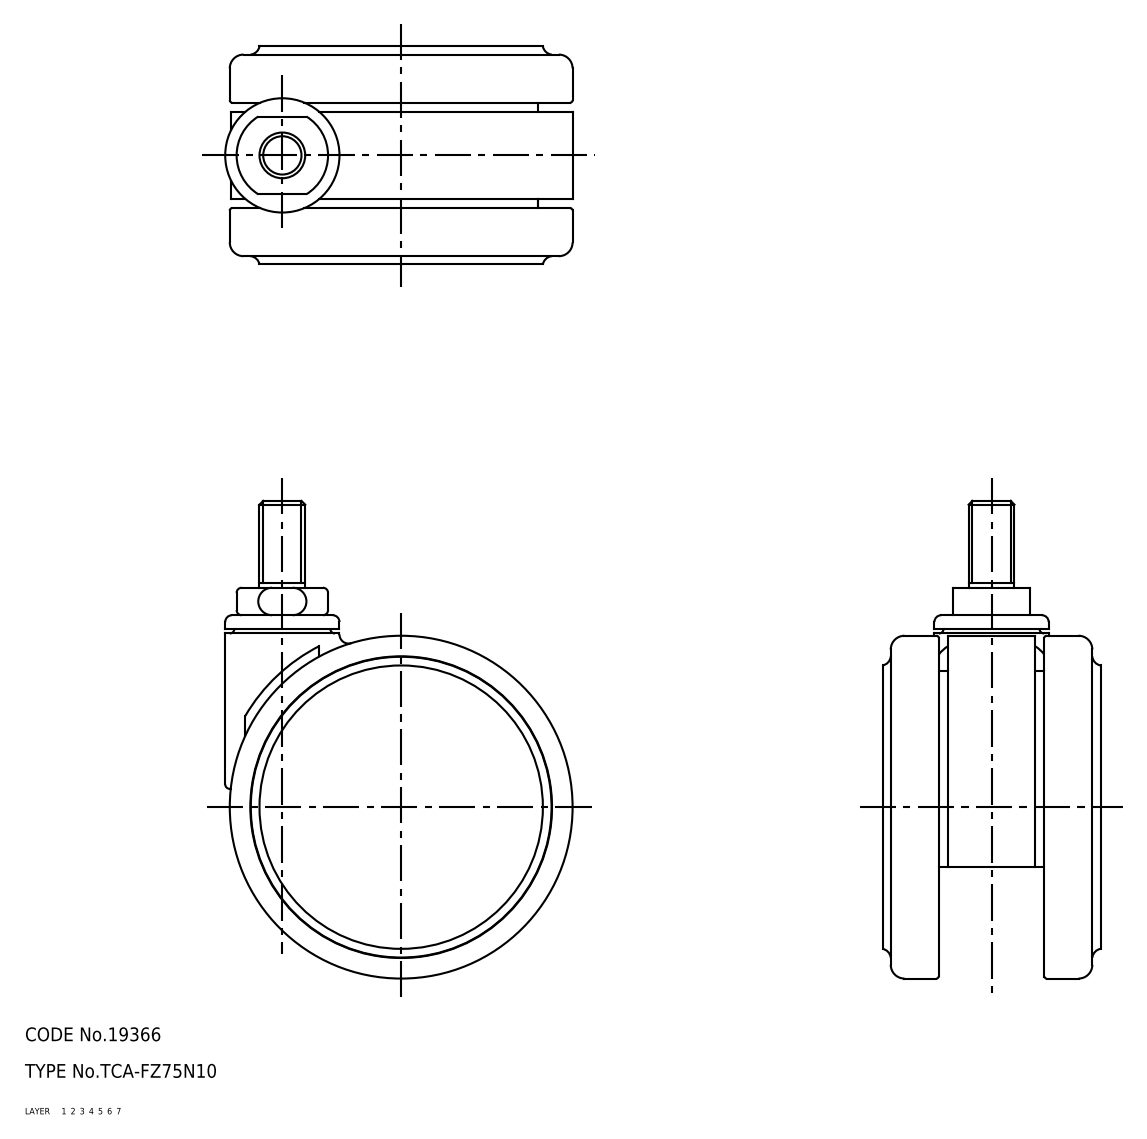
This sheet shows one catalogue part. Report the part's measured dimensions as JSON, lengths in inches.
{"part_name": "caster; TCA-FZ75N10", "step_written_by": "SolidWorks 2015 (AUTOMOTIVE_DESIGN)", "units": "inches", "bodies": {"solids": 1, "faces": 1801, "planar": 425, "cylindrical": 766, "other": 610}, "overall_size": [4.114, 2.992, 1.878], "volume_in3": 6.903, "surface_area_in2": 106.7, "round_holes": [[0.256, 1], [0.315, 1], [0.319, 1], [0.335, 1], [0.402, 1], [0.433, 1], [0.669, 1], [0.713, 1], [0.748, 1], [0.89, 1], [2.323, 1], [2.48, 1]], "round_bosses_or_shafts": [[0.63, 2], [2.591, 1], [2.126, 1], [1.024, 1], [0.984, 1], [0.551, 1], [0.394, 1], [0.315, 1]], "partial_cylinders_radius": [[0.039, 139], [0.02, 133], [0.012, 120], [0.008, 16], [0.079, 12], [0.118, 1], [0.157, 1], [0.236, 1]], "face_to_face_distances": [0.059, 1.819, 0.071, 0.13, 1.748, 1.689, 1.264, 0.354, 0.484, 1.394]}
